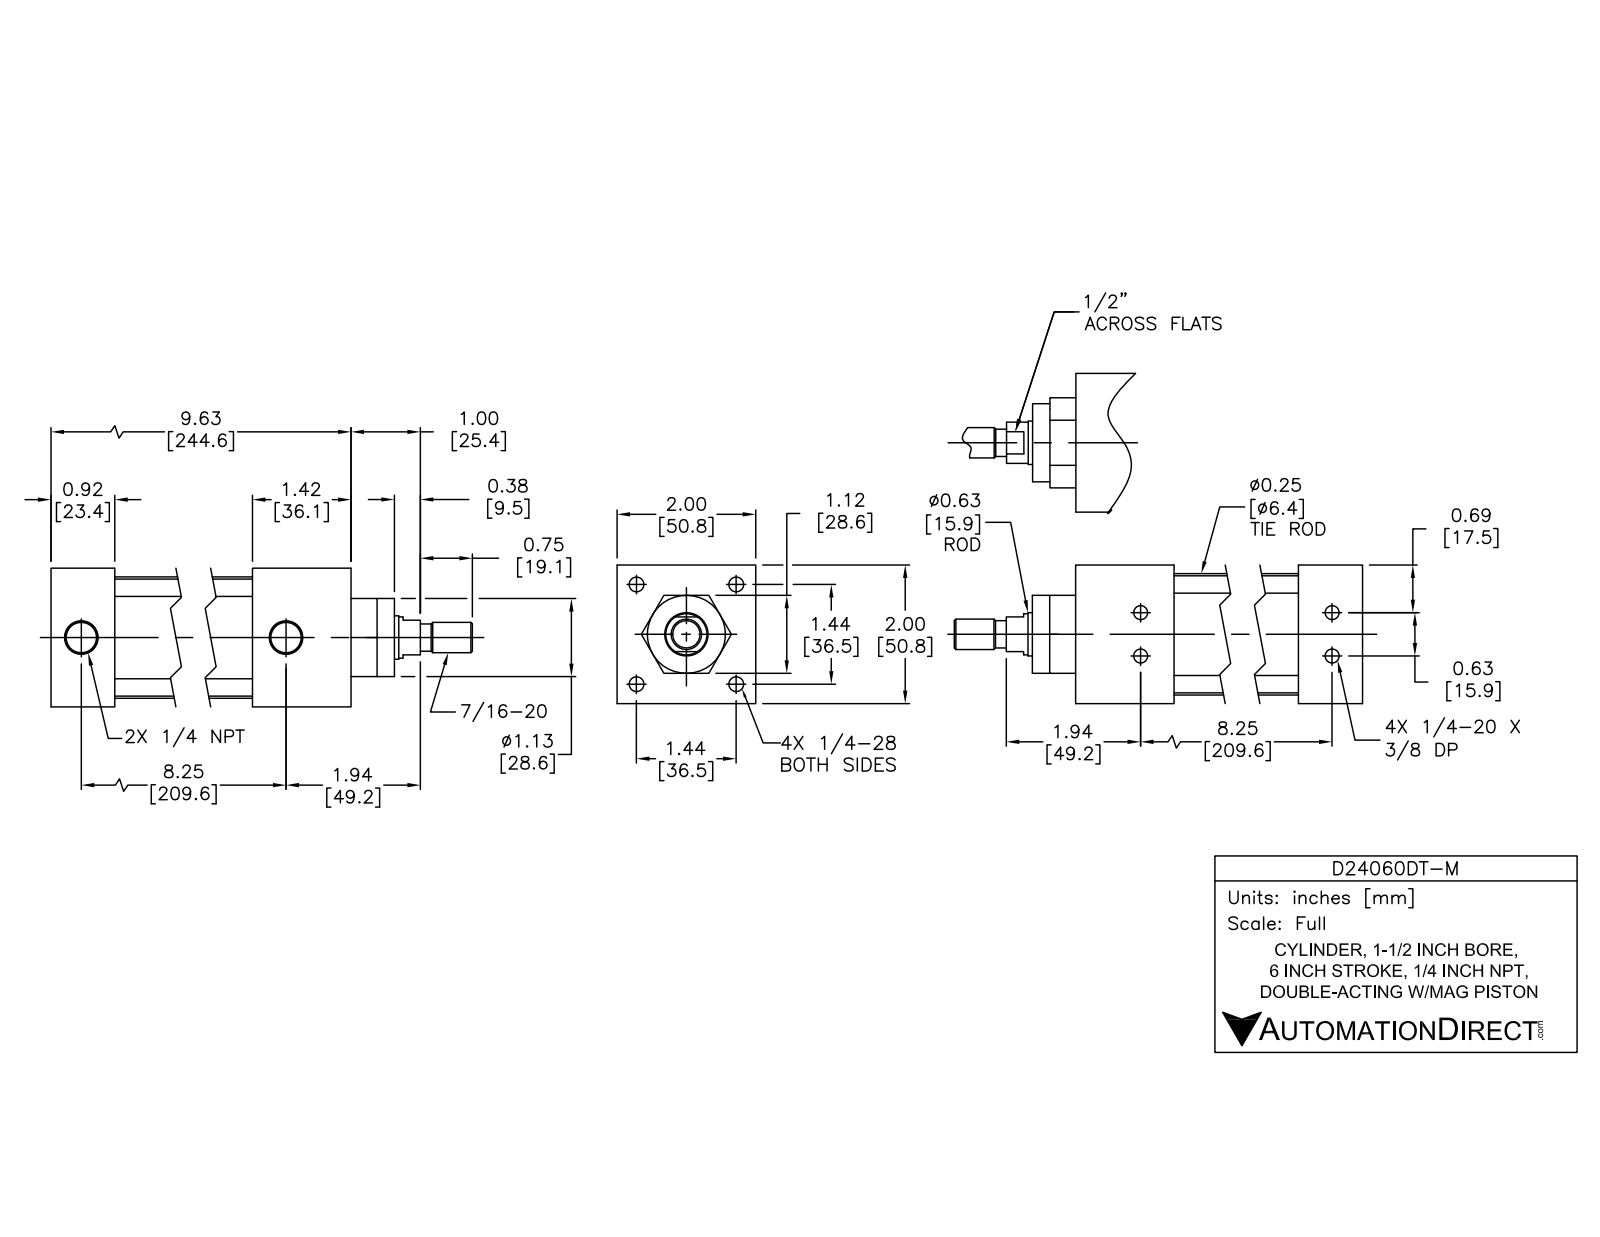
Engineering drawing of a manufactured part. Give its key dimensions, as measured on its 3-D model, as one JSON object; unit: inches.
{"part_name": "D24060DT-M; D24060DT-M BODY; D24060DT-M PISTON", "step_written_by": "SolidWorks 2015 (AUTOMOTIVE_DESIGN)", "units": "inches", "bodies": {"solids": 12, "faces": 303, "planar": 99, "cylindrical": 114, "other": 90}, "overall_size": [11.371, 2, 2], "volume_in3": 19.27, "surface_area_in2": 182.8, "round_holes": [[0.196, 4], [0.211, 4], [0.281, 4], [0.406, 4], [0.297, 2], [0.477, 2], [0.625, 1], [0.628, 1], [1.5, 1]], "round_bosses_or_shafts": [[0.39, 4], [0.25, 4], [0.222, 4], [1.75, 1], [1.497, 1], [1.121, 1], [0.622, 1], [0.59, 1]], "partial_cylinders_radius": [[0.2, 4]], "face_to_face_distances": [2, 9.621, 1.42, 8.201, 8.701, 7.281, 0.92, 1.121, 8.601, 7.181], "hole_center_spacings": [0.313, 1.014, 1.434, 0.625, 2.028, 8.247, 8.252, 8.252]}
